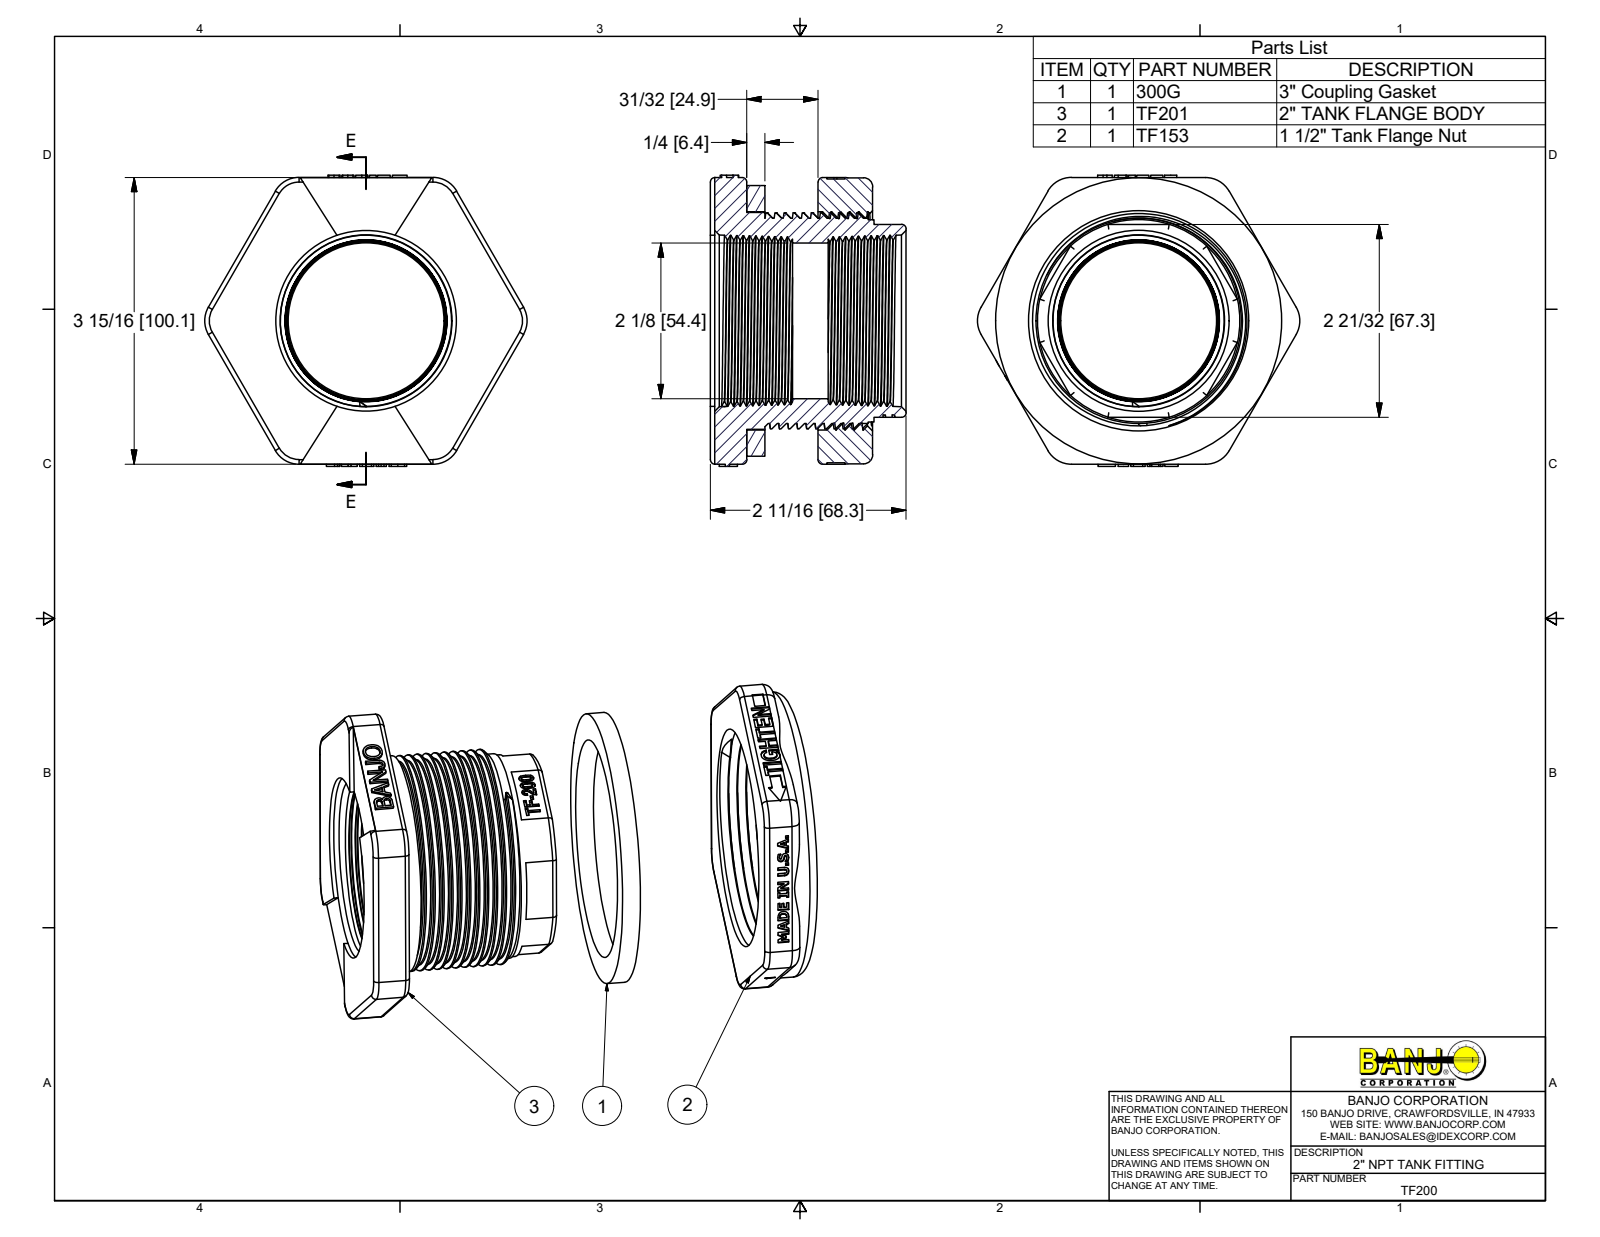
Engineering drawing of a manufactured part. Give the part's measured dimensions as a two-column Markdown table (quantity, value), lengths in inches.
| quantity | value |
| --- | --- |
| part name | TF200; TF201; TF153; TF153X (+1 more) |
| STEP written by | Autodesk Inventor 2017 (AUTOMOTIVE_DESIGN) |
| units | inches |
| bodies | 3 solids, 854 faces (494 planar, 76 cylindrical, 284 other) |
| overall size | 4.433 × 4.002 × 2.69 |
| volume | 15.42 in³ |
| surface area | 130.2 in² |
| round holes (diameter × count) | 2.14 × 1, 2.807 × 1, 3 × 1 |
| round bosses / shafts (diameter × count) | 3.93 × 1, 3.719 × 1, 2.98 × 1, 2.97 × 1, 2.82 × 1, 2.78 × 1 |
| partial cylindrical surfaces (radius × count) | 0.063 × 24, 0.125 × 6, 0.375 × 6, 0.01 × 1, 0.846 × 1, 1.243 × 1 |
| main face-to-face distances | 1.48, 0.75, 0.5, 0.98, 0.25, 0.73, 1.73, 2.23, 3.94, 0.44 |
